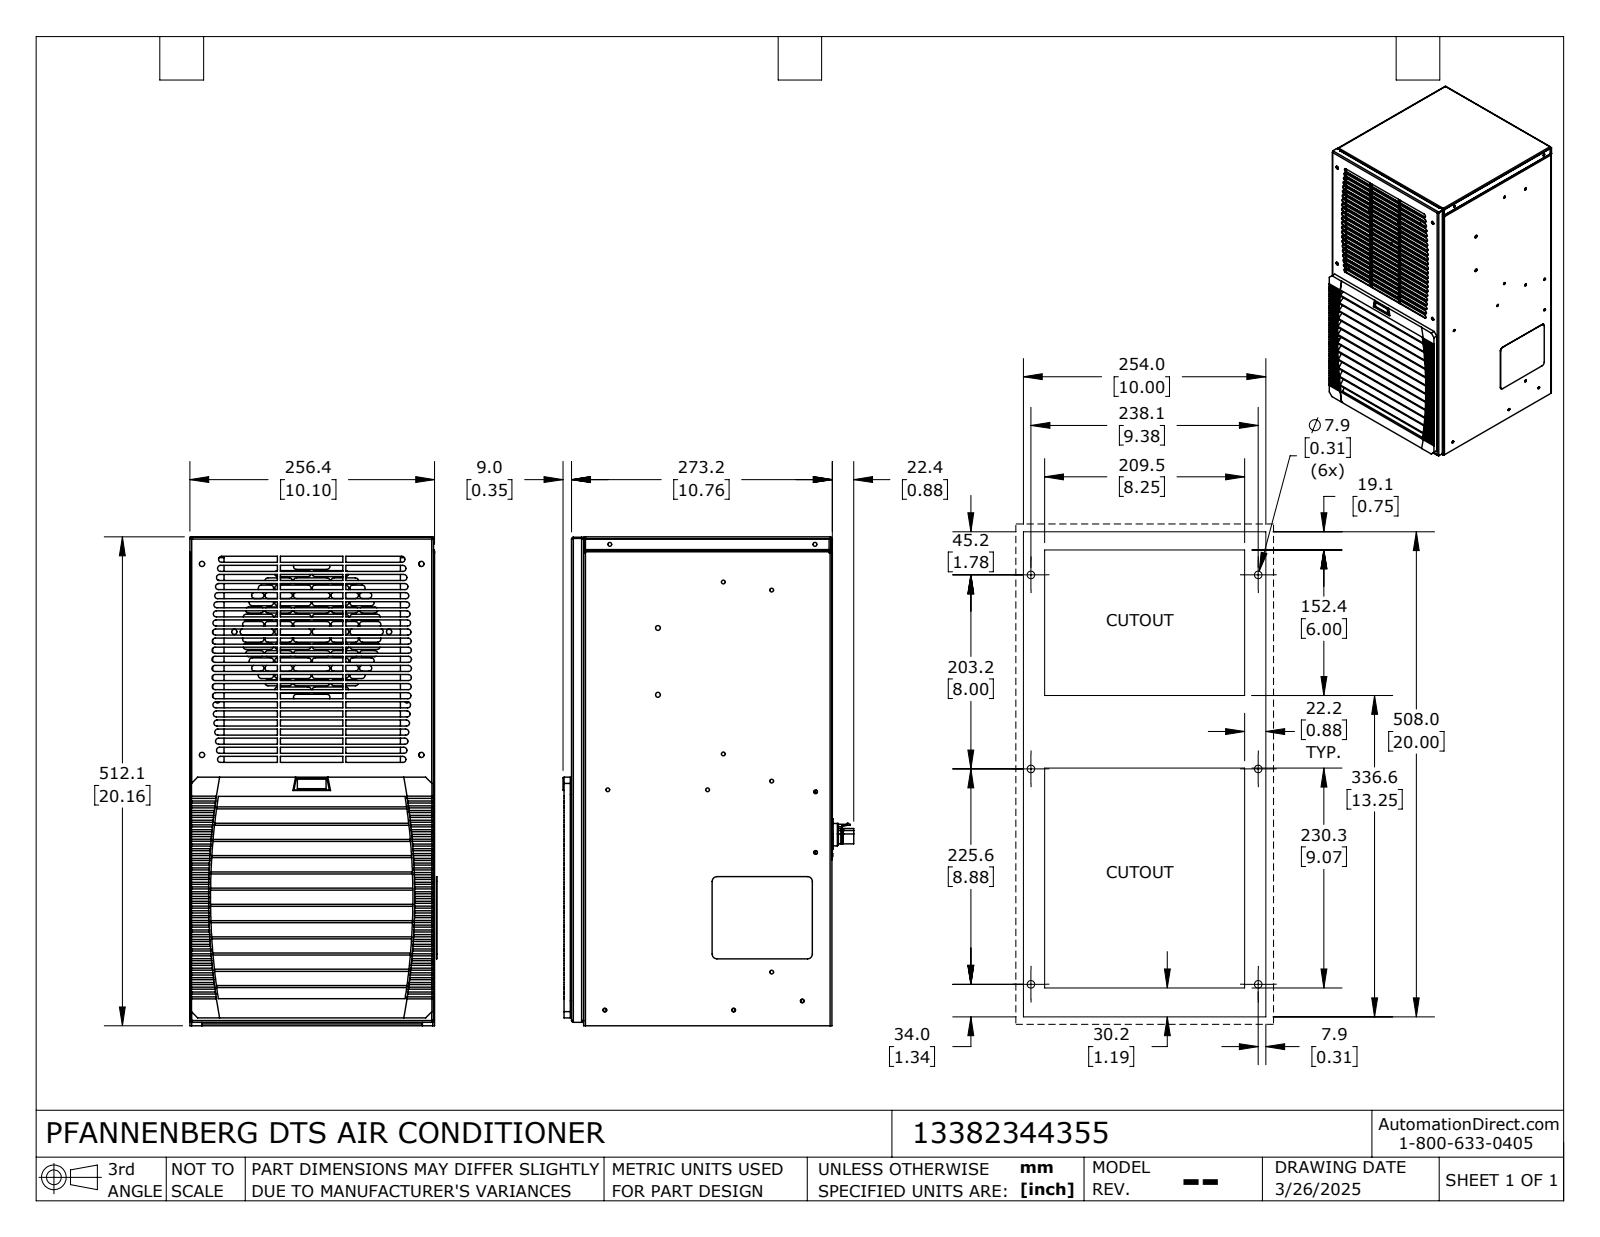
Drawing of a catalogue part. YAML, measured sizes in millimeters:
part_name: "13382344355_Default"
step_written_by: "SolidWorks 2024 (CONFIG_CONTROL_DESIGN)"
units: millimeters
bodies: {solids: 11, faces: 2383, planar: 1378, cylindrical: 900, other: 105}
overall_size: [512.1, 304.5, 258.6]
volume: 1762000
surface_area: 1635000
round_holes:
  - {diameter: 4, count: 12}
  - {diameter: 4, count: 12}
  - {diameter: 5.5, count: 12}
  - {diameter: 4.7, count: 8}
  - {diameter: 4.2, count: 6}
  - {diameter: 4.3, count: 5}
  - {diameter: 5.3, count: 5}
  - {diameter: 3.8, count: 4}
  - {diameter: 7.1, count: 4}
  - {diameter: 8, count: 4}
  - {diameter: 10, count: 4}
  - {diameter: 3.3, count: 3}
round_bosses_or_shafts:
  - {diameter: 2, count: 4}
  - {diameter: 12.1, count: 2}
  - {diameter: 35, count: 1}
  - {diameter: 28, count: 1}
  - {diameter: 24, count: 1}
  - {diameter: 23, count: 1}
  - {diameter: 14.2, count: 1}
partial_cylinders:
  - {radius: 3.2, count: 186}
  - {radius: 3, count: 43}
  - {radius: 0.8, count: 30}
  - {radius: 1.9, count: 30}
  - {radius: 1.2, count: 24}
  - {radius: 0.8, count: 10}
  - {radius: 1.9, count: 10}
  - {radius: 2, count: 8}
face_to_face_distances: [1.1, 1.1, 254.2, 255.3, 255.3, 256.4, 272.1, 12, 1.4, 270.6]
hole_center_spacings: [125, 63.5, 27.5, 70, 75.2, 197.3, 233.6, 1.3]
